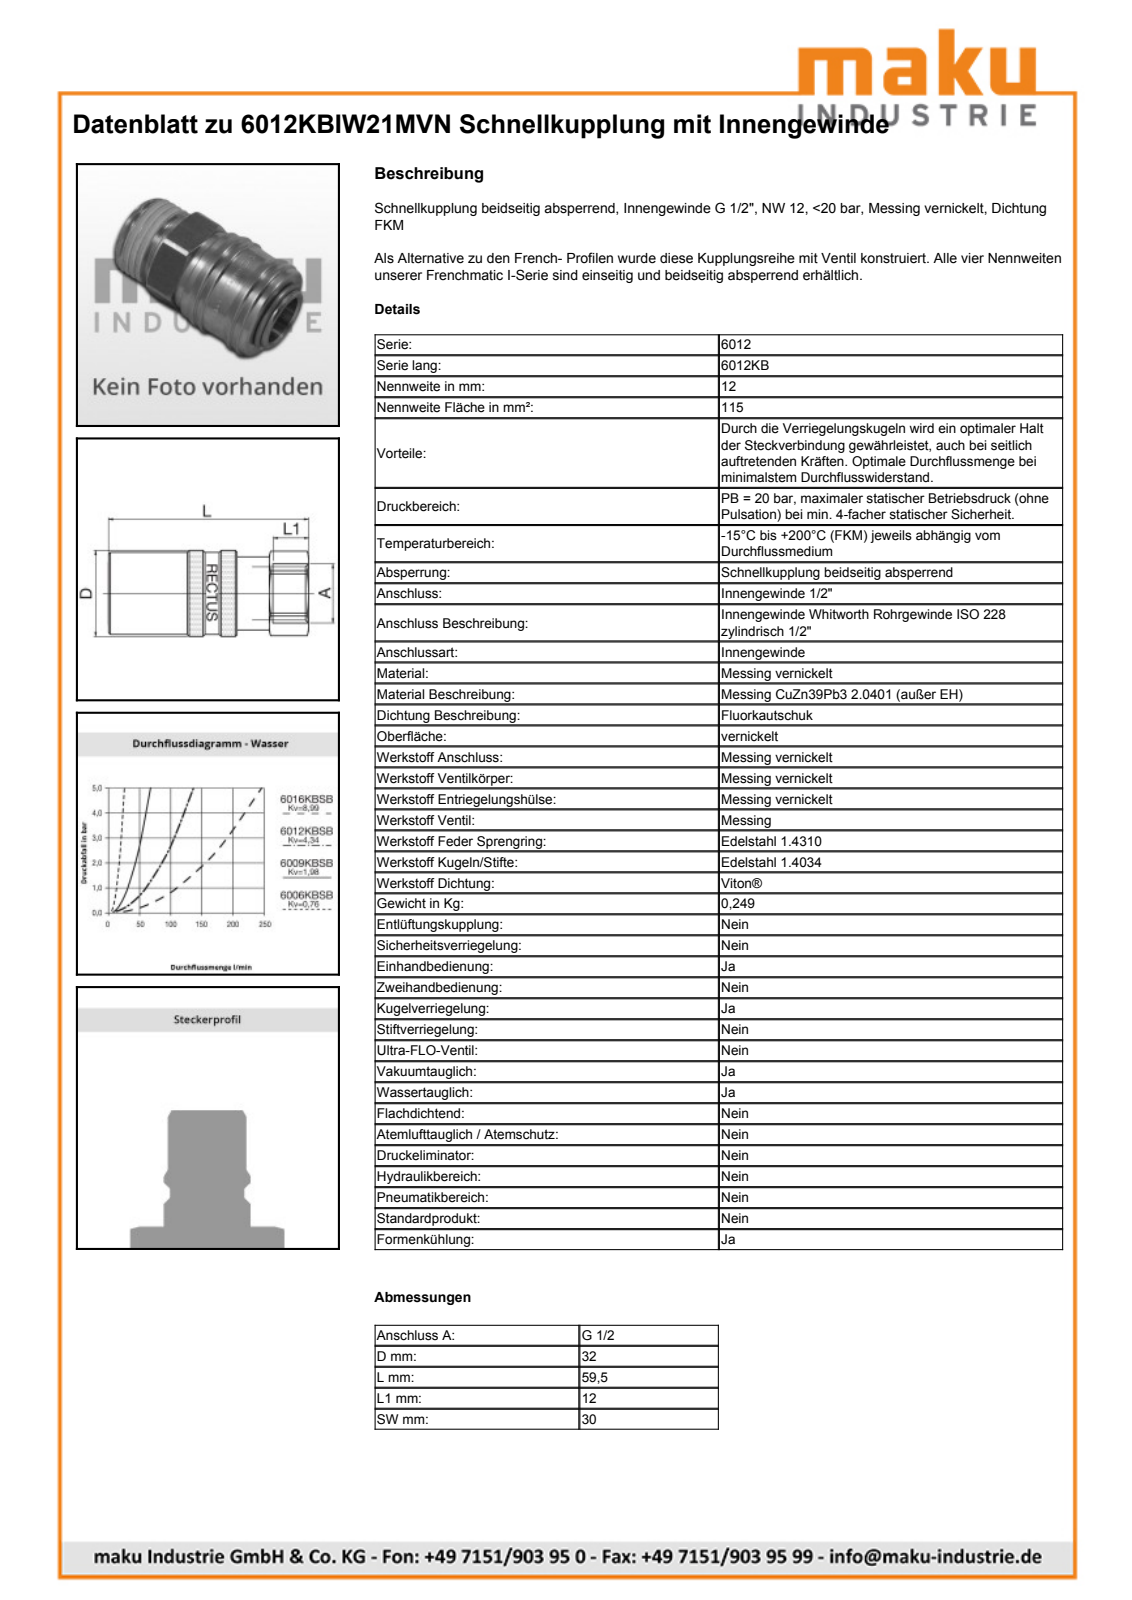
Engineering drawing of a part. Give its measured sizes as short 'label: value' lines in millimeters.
name: D107359
written by: Autodesk Inventor 2013 (AUTOMOTIVE_DESIGN)
unit: mm
bodies: 2 solids, 633 faces (198 planar, 74 cylindrical, 361 other)
size: 69.5 × 33.72 × 32
volume: 45 443 mm³; area: 17 565 mm²
holes: 1× ⌀20.95, 1× ⌀24.2, 1× ⌀26.4, 1× ⌀29.3
bosses: 1× ⌀32, 1× ⌀31, 1× ⌀30.8, 1× ⌀29, 1× ⌀28, 1× ⌀26.41, 1× ⌀24, 1× ⌀22.5
rounds: 1× R11.55, 1× R16.93
face distances: 30, 58.37, 11.13, 69.5, 30.02, 56.5, 45.37, 13, 24, 34.37
